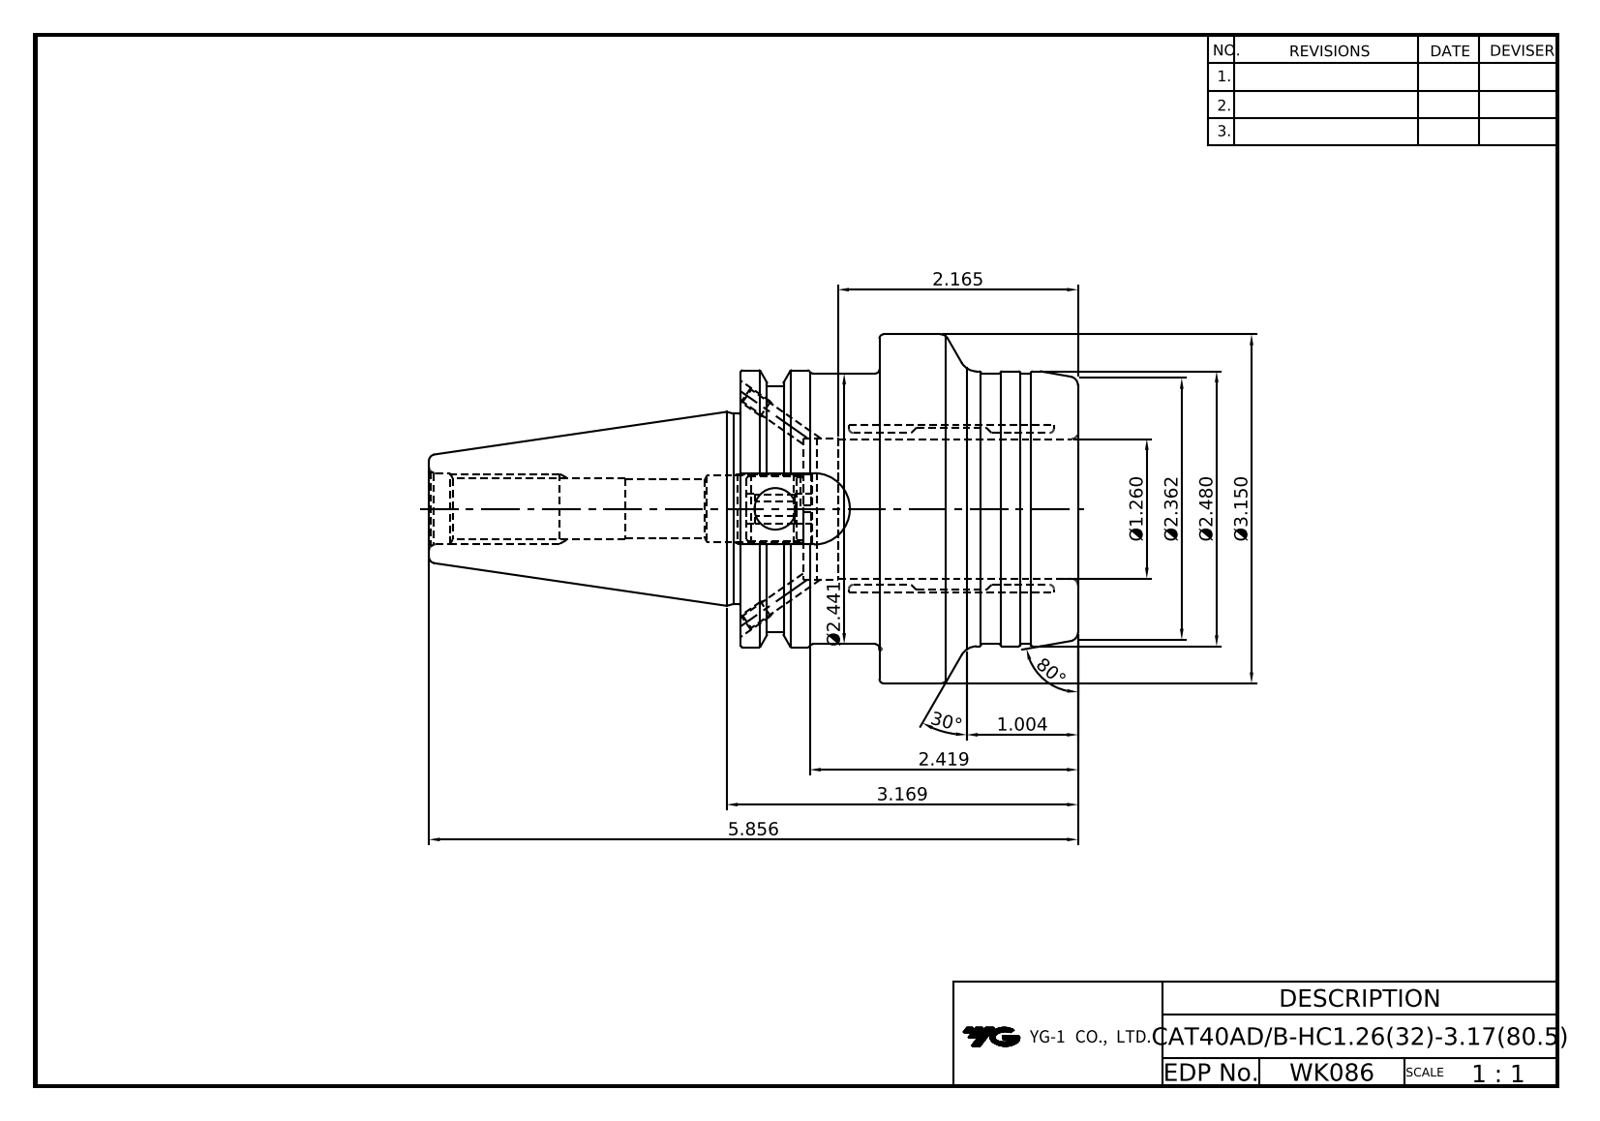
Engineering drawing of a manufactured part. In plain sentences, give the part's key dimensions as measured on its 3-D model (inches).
The part is named "LO-CAT40ADB-HC32-80.5". Its 3-D file was written by "Autodesk Inventor 2020 (AUTOMOTIVE_DESIGN)". It is 1 solid with 105 faces: 30 planar, 28 cylindrical and 47 other. Overall it measures 5.856 by 3.15 by 3.15 inches. Its volume is 16.65 cubic inches and its surface area 66.54 square inches. Round holes: 2 of diameter 0.128, 2 of diameter 0.157, 1 of diameter 0.315, 1 of diameter 0.375, 1 of diameter 0.527, 1 of diameter 0.587, 1 of diameter 0.642, 1 of diameter 1.26, 1 of diameter 1.283. Round bosses or shafts: 1 of diameter 3.15, 1 of diameter 2.5, 1 of diameter 2.48, 1 of diameter 2.441, 1 of diameter 2.217, 1 of diameter 1.717. Partial cylindrical surfaces (rounded edges, fillets, slot ends): 1 of radius 0.322. The main face-to-face distances are 1.791, 1.253, 3.044, 0.564, 0.689, 2.48, 1.874, 0.645, 2.812, 3.376.
